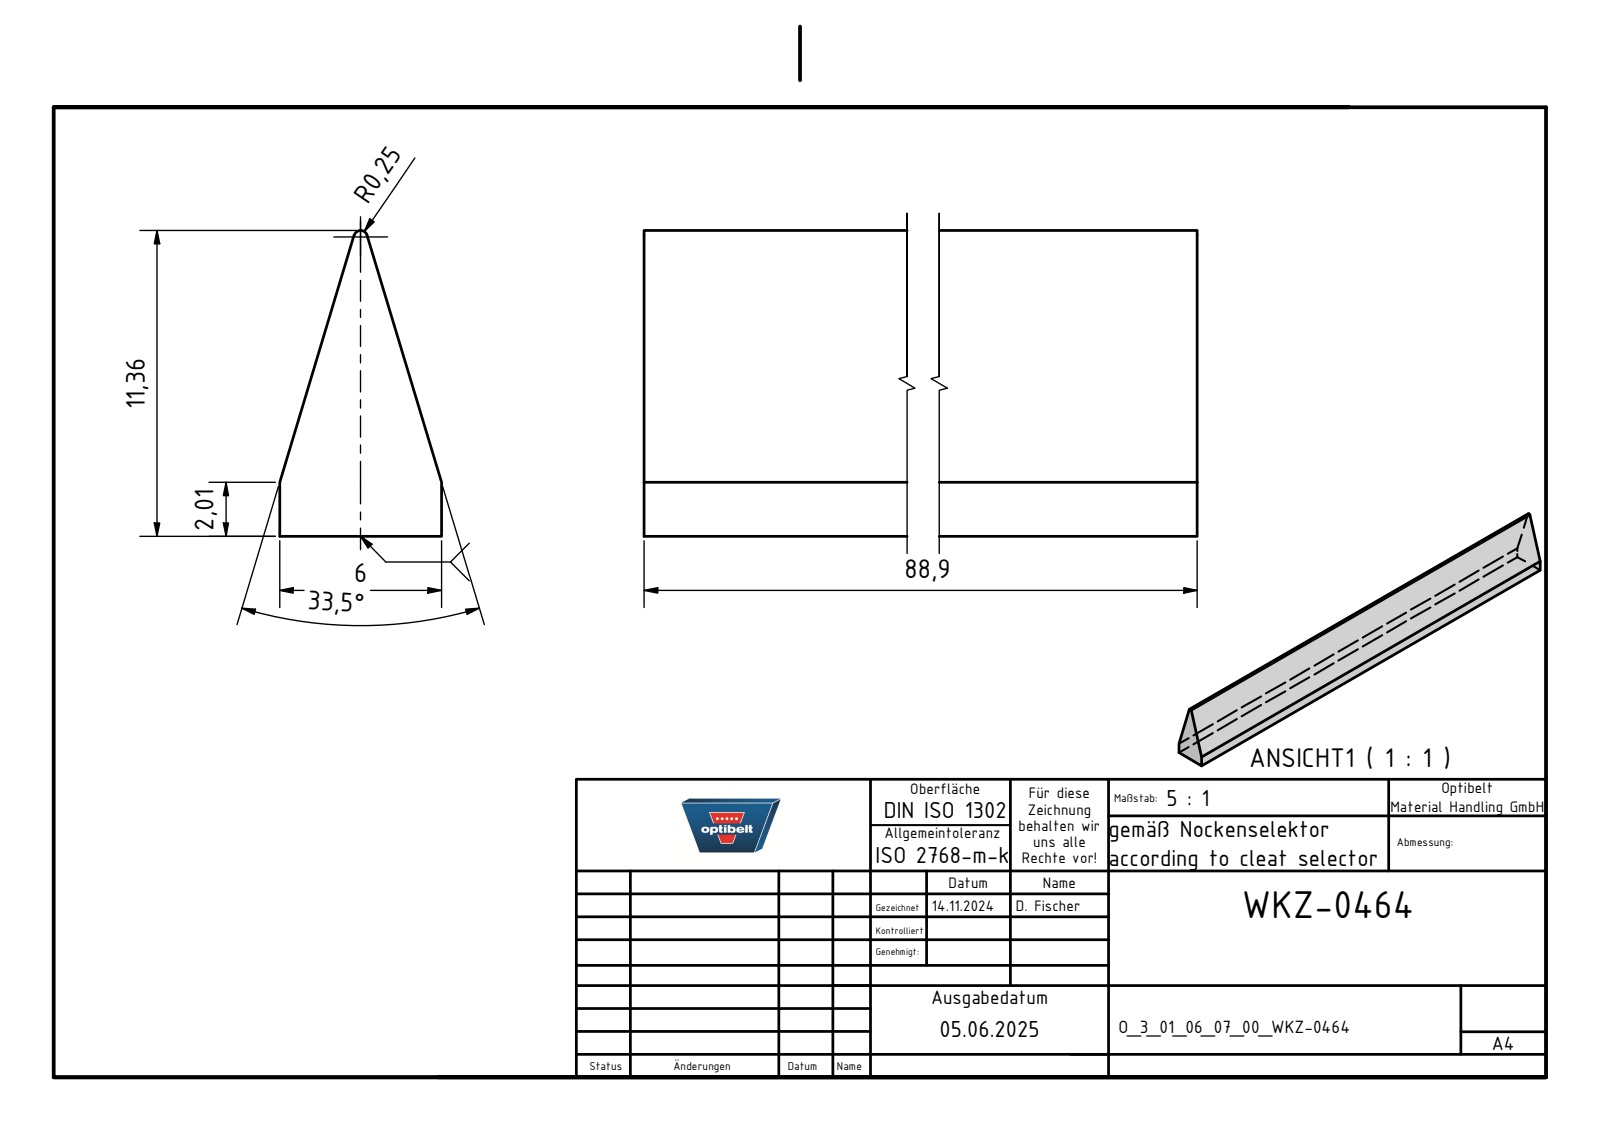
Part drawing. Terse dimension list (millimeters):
name: O_3_01_06_07_00_WKZ-0464
written by: Autodesk Inventor 2025 (AUTOMOTIVE_DESIGN)
unit: mm
bodies: 1 solid, 8 faces (7 planar, 1 cylindrical, 0 other)
size: 88.9 × 11.36 × 6
volume: 3 719 mm³; area: 2 734 mm²
rounds: 1× R0.25
face distances: 6, 88.9
